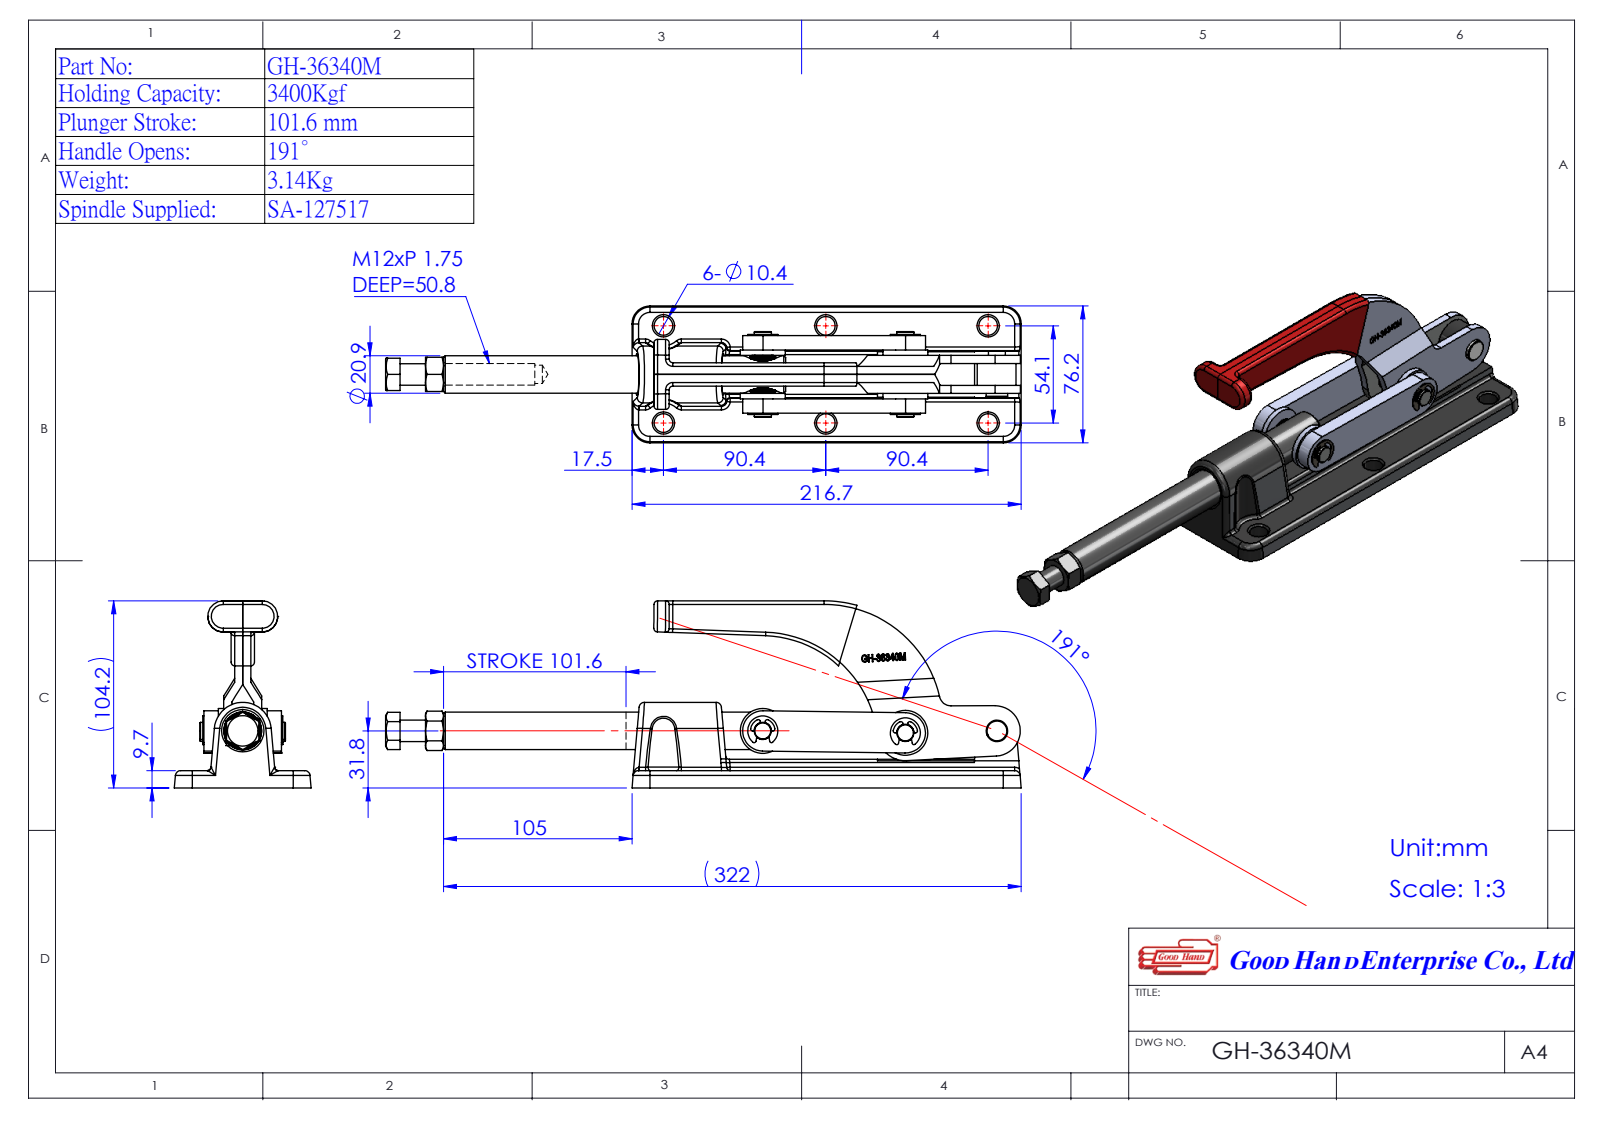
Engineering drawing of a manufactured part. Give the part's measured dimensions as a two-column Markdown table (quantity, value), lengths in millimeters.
| quantity | value |
| --- | --- |
| part name | Group1^GH-36340M(簡化); Group2^GH-36340M(簡化); Group5^GH-36340M(簡化); 33634013-1^GH-36340M(簡化) (+2 more) |
| STEP written by | SolidWorks 2016 (AUTOMOTIVE_DESIGN) |
| units | millimeters |
| bodies | 5 solids, 402 faces (124 planar, 176 cylindrical, 102 other) |
| overall size | 353.9 × 104.19 × 76.2 |
| volume | 407 180 mm³ |
| surface area | 109 955 mm² |
| round holes (diameter × count) | 10.4 × 6, 9 × 1, 10.2 × 1, 21.2 × 1 |
| round bosses / shafts (diameter × count) | 25 × 2, 12 × 2, 9 × 2, 7 × 2, 20.88 × 1, 9.4 × 1 |
| partial cylindrical surfaces (radius × count) | 3 × 10, 2 × 9, 1.08 × 8, 1 × 4, 3.6 × 2, 6.87 × 2, 8.37 × 2, 11.2 × 2 |
| main face-to-face distances | 17.1, 9.7, 15.1, 11, 4.5, 16.7, 4.1, 12.6, 0.4, 32.2 |
| hole center spacings | 90.4, 105.35, 54.1, 180.8, 188.72 |
